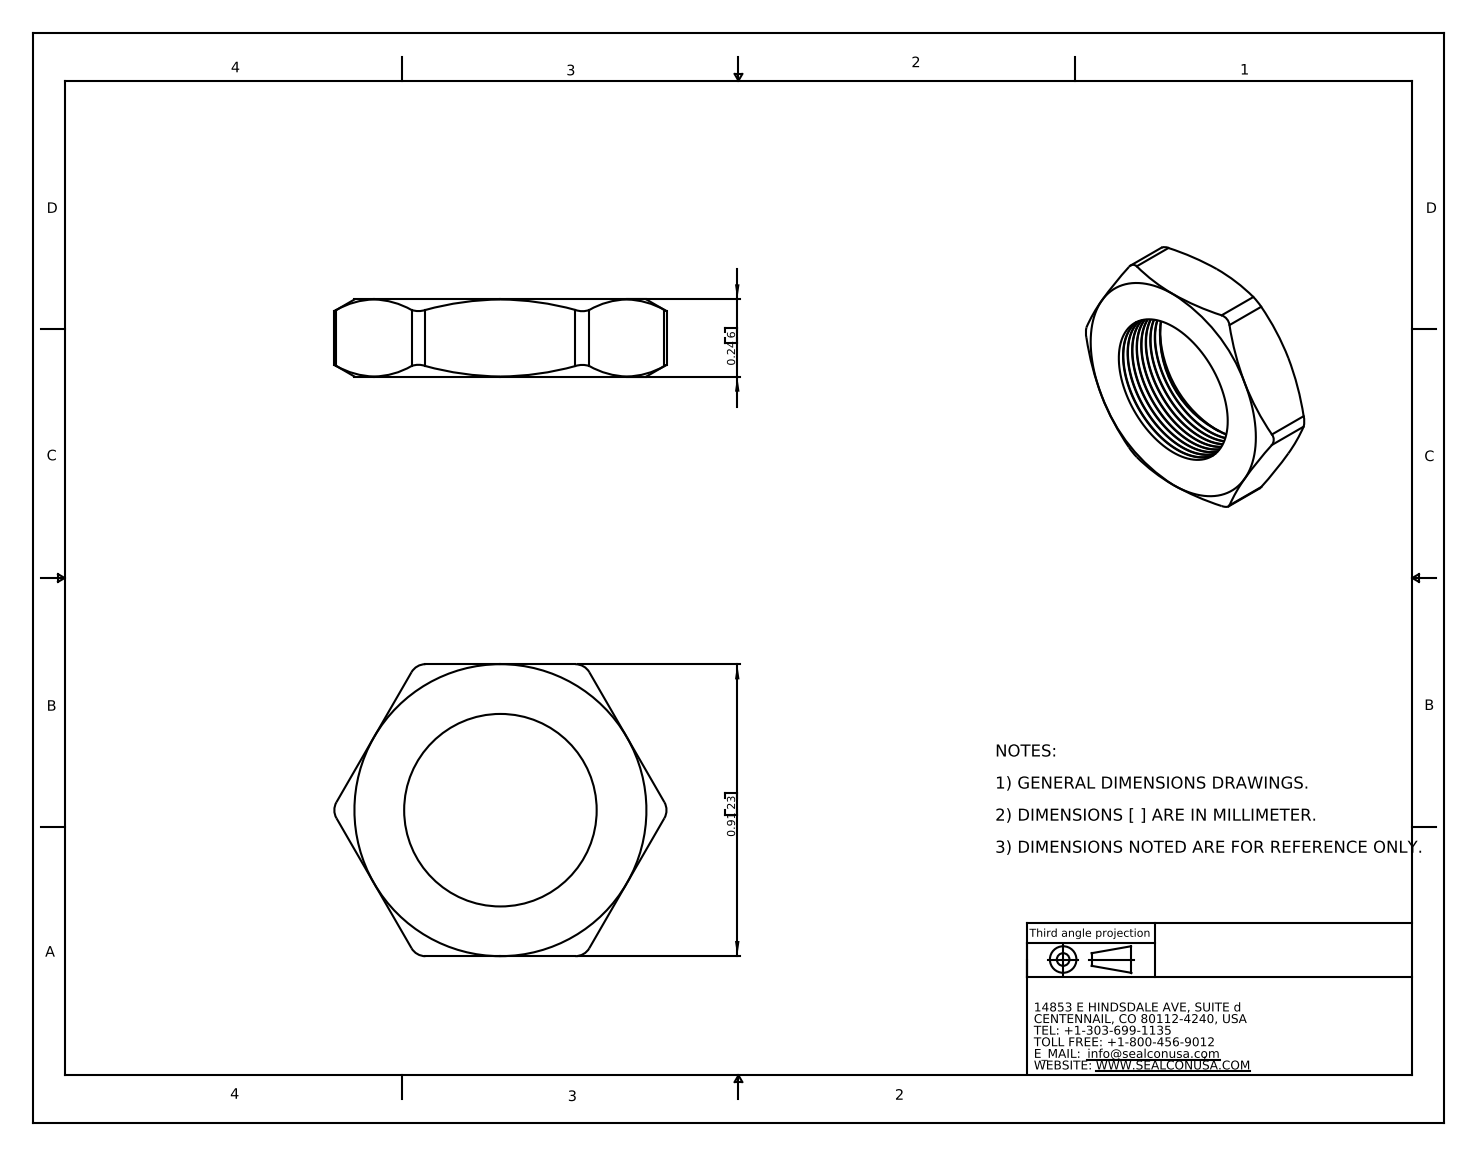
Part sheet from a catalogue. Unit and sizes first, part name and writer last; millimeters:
Units: millimetres
Overall size (bounding box): 26.3 × 23.1 × 6.1
Round holes (diameter × count): ⌀15.2 ×1
Partial cylindrical surfaces — rounded edges, fillets, slot ends (radius × count): R1.3 ×6
Main face-to-face distances: 6.1, 23.1
Volume: 1 600 mm³ · Surface area: 1 565 mm²
Bodies: 1 solid, 87 faces (8 planar, 25 cylindrical, 54 other)
Part name (STEP PRODUCT): NP-09
STEP written by: SolidWorks 2007 (CONFIG_CONTROL_DESIGN)
